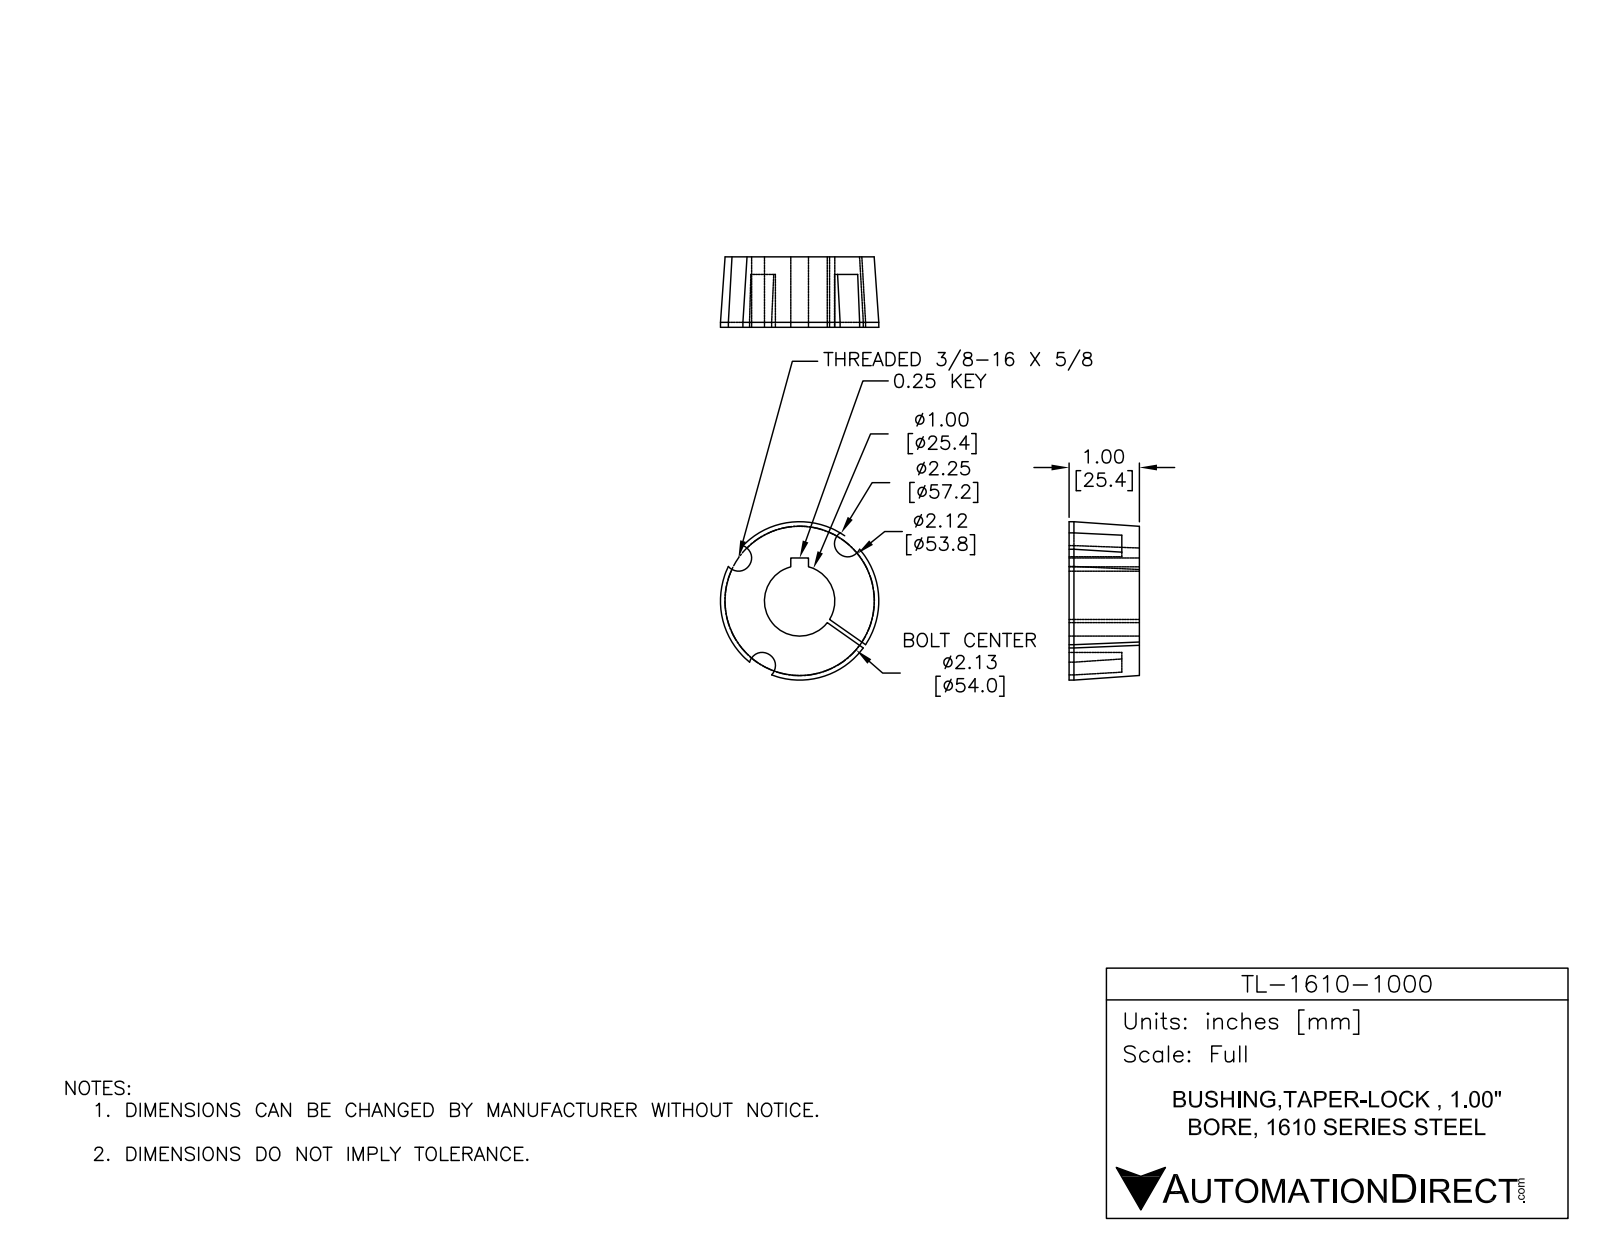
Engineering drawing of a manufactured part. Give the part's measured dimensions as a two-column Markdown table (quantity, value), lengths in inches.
| quantity | value |
| --- | --- |
| part name | TL-1610-1000 |
| STEP written by | SolidWorks 2014 (AUTOMOTIVE_DESIGN) |
| units | inches |
| bodies | 1 solid, 24 faces (9 planar, 12 cylindrical, 3 other) |
| overall size | 2.25 × 2.25 × 1 |
| volume | 2.751 in³ |
| surface area | 17.66 in² |
| round holes (diameter × count) | 1 × 1 |
| round bosses / shafts (diameter × count) | 2.25 × 1 |
| partial cylindrical surfaces (radius × count) | 0.188 × 3 |
| main face-to-face distances | 1, 0.057, 0.25, 0.75 |
